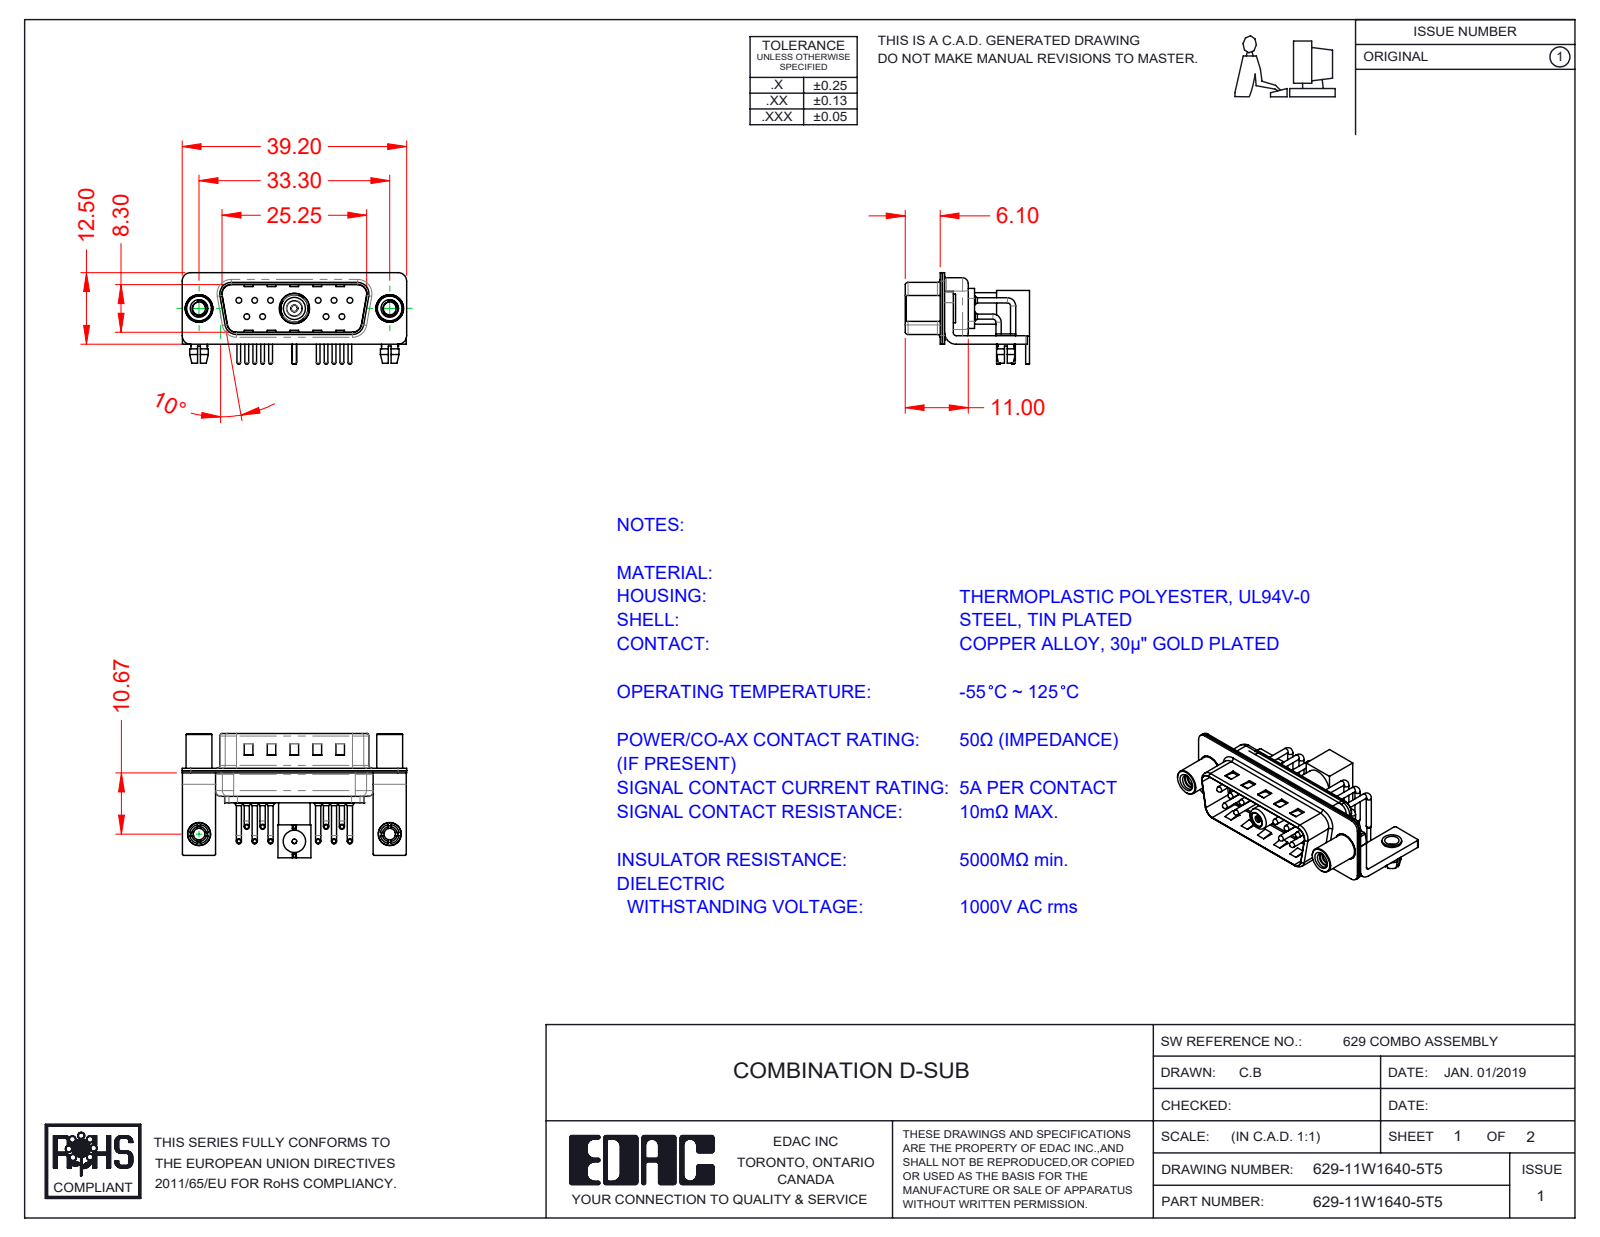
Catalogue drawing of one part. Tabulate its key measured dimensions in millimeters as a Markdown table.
| quantity | value |
| --- | --- |
| part name | Insulator RA Pin; Socket_RA; Co-Ax Jack Assy_RA; 629Combo Shell Front_15 Contacts (+8 more) |
| STEP written by | SolidWorks 2020 (CONFIG_CONTROL_DESIGN) |
| units | millimeters |
| bodies | 26 solids, 1785 faces (915 planar, 656 cylindrical, 214 other) |
| overall size | 39.2 × 21.71 × 16 |
| volume | 2 644 mm³ |
| surface area | 7 203 mm² |
| round holes (diameter × count) | 2 × 12, 1.6 × 11, 0.75 × 10, 2.5 × 3, 2.26 × 2, 3.2 × 2, 4 × 2, 4.8 × 2, 0.8 × 1, 1.1 × 1, 1.2 × 1, 1.5 × 1 |
| round bosses / shafts (diameter × count) | 0.9 × 20, 1.5 × 10, 1 × 10, 0.65 × 10, 4 × 3, 3.3 × 3, 2.9 × 3, 5 × 2 |
| partial cylindrical surfaces (radius × count) | 0.25 × 16, 1.5 × 16, 2 × 13, 1.01 × 10, 0.5 × 9, 1.6 × 8, 1 × 7, 0.6 × 4 |
| main face-to-face distances | 0.4, 0.8, 1.5, 9.5, 9.1, 8.7, 9.9, 0.6, 1.9, 0.35 |
| hole center spacings | 3.16, 2.77, 13.85, 16.7, 11.08, 16.62, 5.03, 5.04 |
